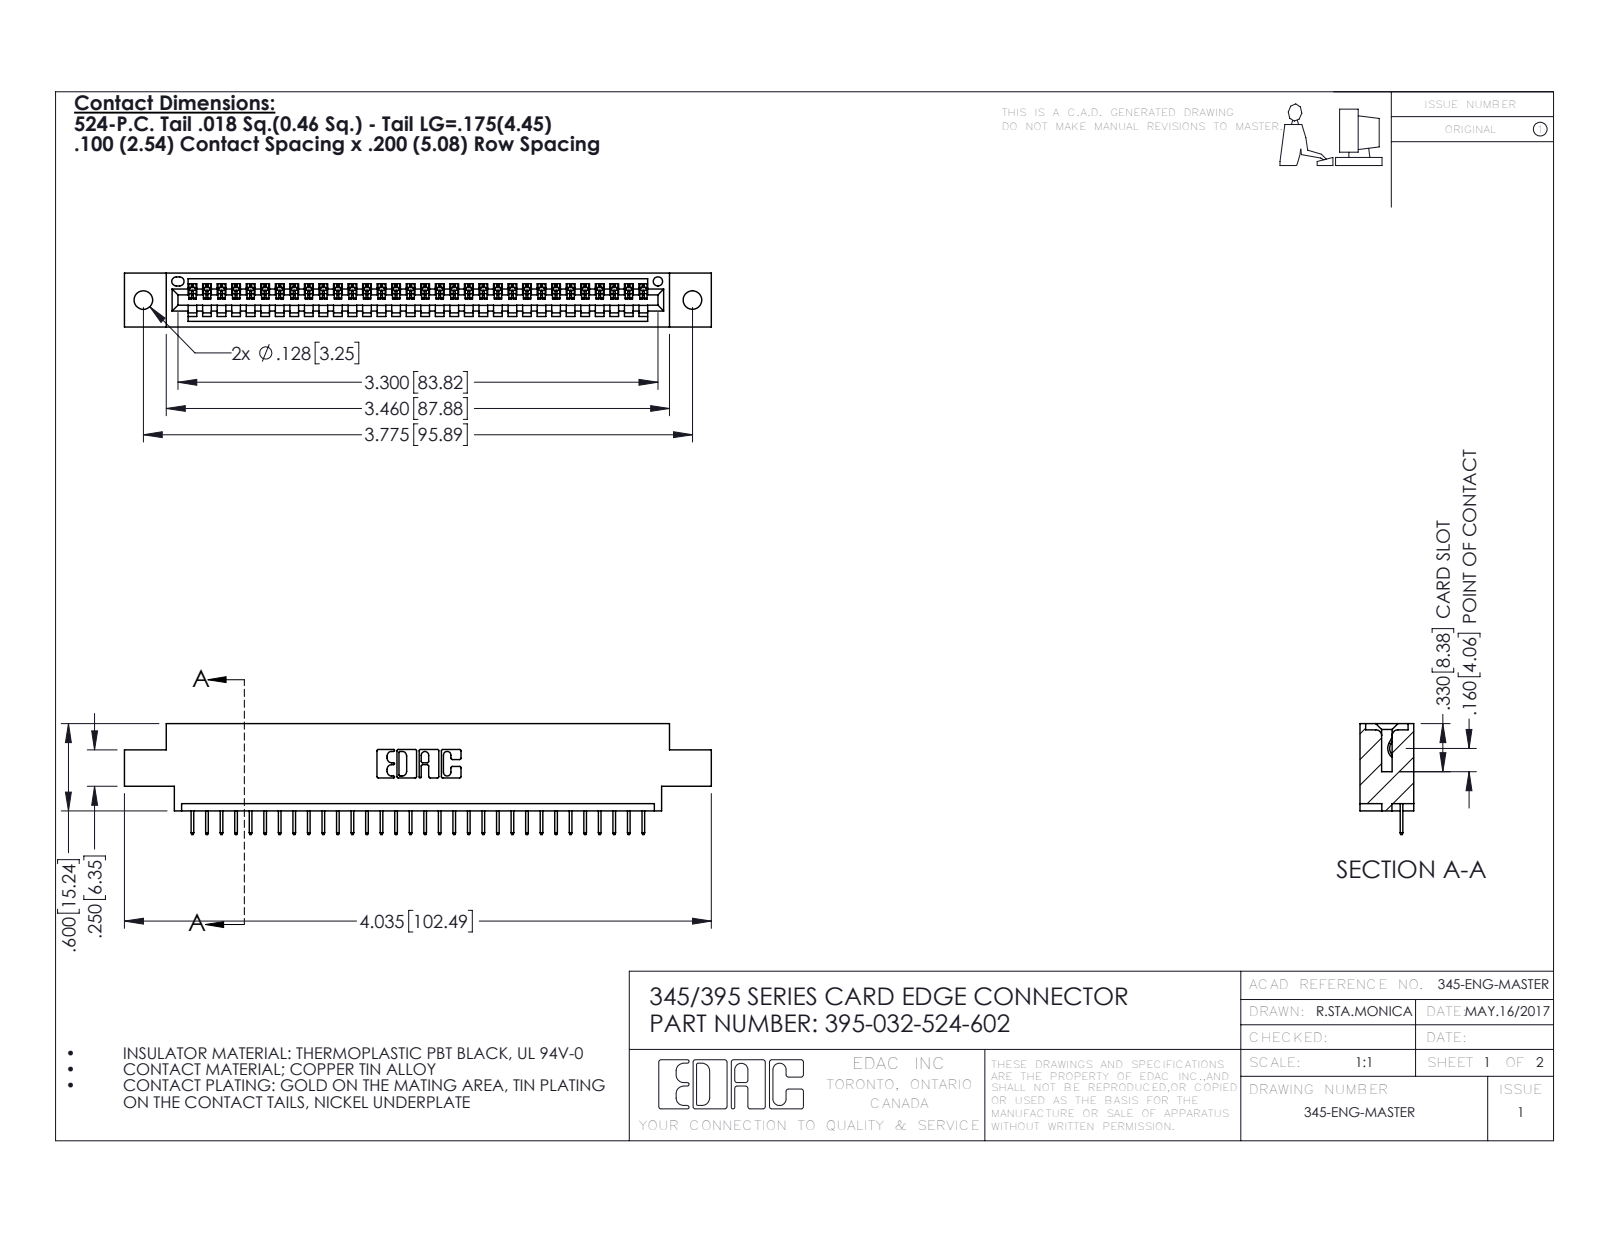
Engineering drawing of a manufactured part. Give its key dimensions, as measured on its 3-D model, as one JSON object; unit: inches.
{"part_name": "345 Part_0.170 Offset - 0.128 Dia; 345-292-001_345-293-124; 395-032-524-602", "step_written_by": "SolidWorks 2016 (CONFIG_CONTROL_DESIGN)", "units": "inches", "bodies": {"solids": 33, "faces": 2114, "planar": 1556, "cylindrical": 558, "other": 0}, "overall_size": [4.035, 0.762, 0.37], "volume_in3": 0.572, "surface_area_in2": 18.25, "round_holes": [[0.128, 2], [0.064, 1]], "partial_cylinders_radius": [[0.006, 64], [0.01, 22], [0.007, 6], [0.031, 6], [0.026, 3], [0.031, 2], [0.04, 2], [0.014, 1]], "face_to_face_distances": [0.072, 0.298, 0.37, 0.2, 0.098, 0.272, 0.025, 0.225, 0.072, 0.175], "hole_center_spacings": [0.27, 3.54, 3.775]}
